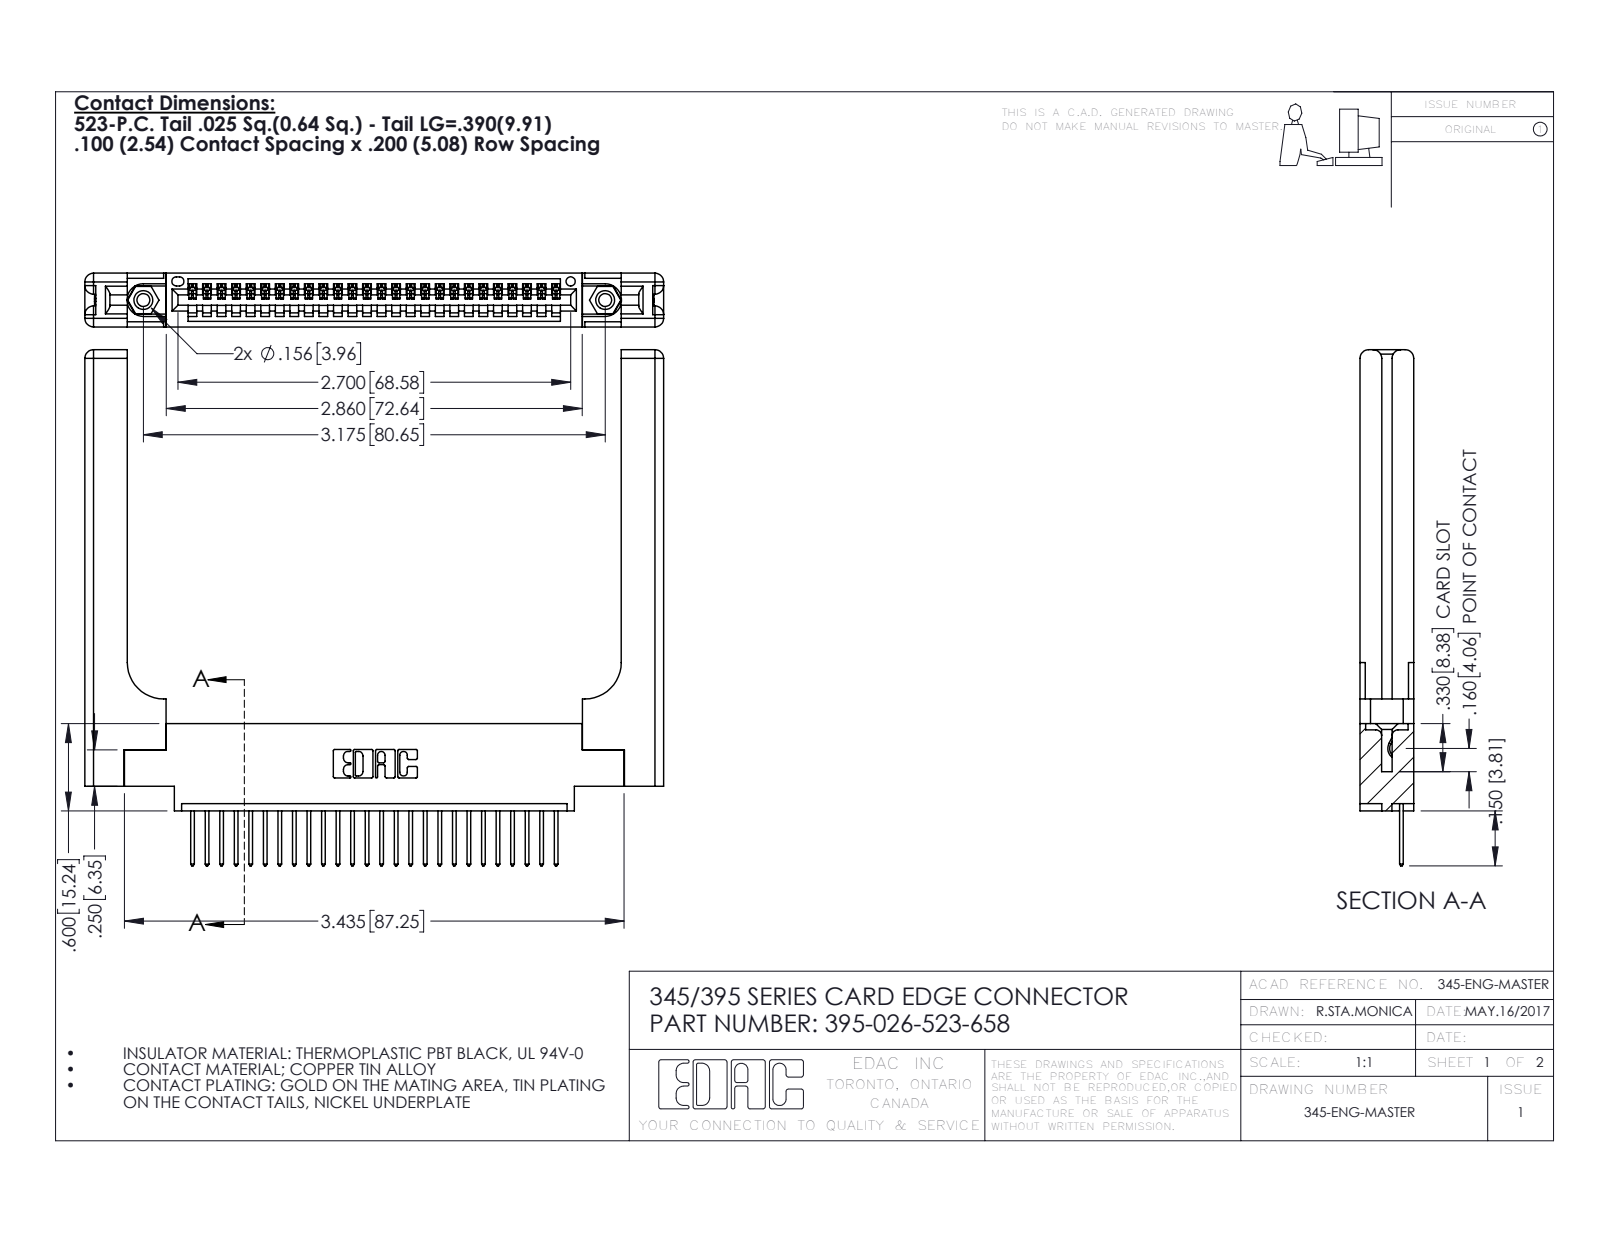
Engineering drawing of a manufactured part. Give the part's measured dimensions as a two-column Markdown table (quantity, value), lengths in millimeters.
| quantity | value |
| --- | --- |
| part name | 345-220-058_345-220-058; 345-250-001_345-250-001-102; 345 Part_0.170 Offset - 0.156 Dia-TH; 395-026-523-658 (+1 more) |
| STEP written by | SolidWorks 2016 (CONFIG_CONTROL_DESIGN) |
| units | millimeters |
| bodies | 31 solids, 1894 faces (1272 planar, 562 cylindrical, 60 other) |
| overall size | 101.1 × 90.1 × 9.4 |
| volume | 17 850 mm³ |
| surface area | 17 660 mm² |
| round holes (diameter × count) | 2.3 × 2, 3.2 × 2, 4 × 2, 1.6 × 1 |
| round bosses / shafts (diameter × count) | 3.9 × 2 |
| partial cylindrical surfaces (radius × count) | 0.2 × 52, 0.3 × 52, 0.3 × 22, 1.5 × 16, 0.2 × 6, 0.8 × 6, 0.7 × 3, 0.8 × 2 |
| main face-to-face distances | 9.4, 1.8, 7.6, 2.5, 6.9, 0.6, 3.8, 3.8, 5.1, 2 |
| hole center spacings | 6.9, 74.7, 80.6 |
